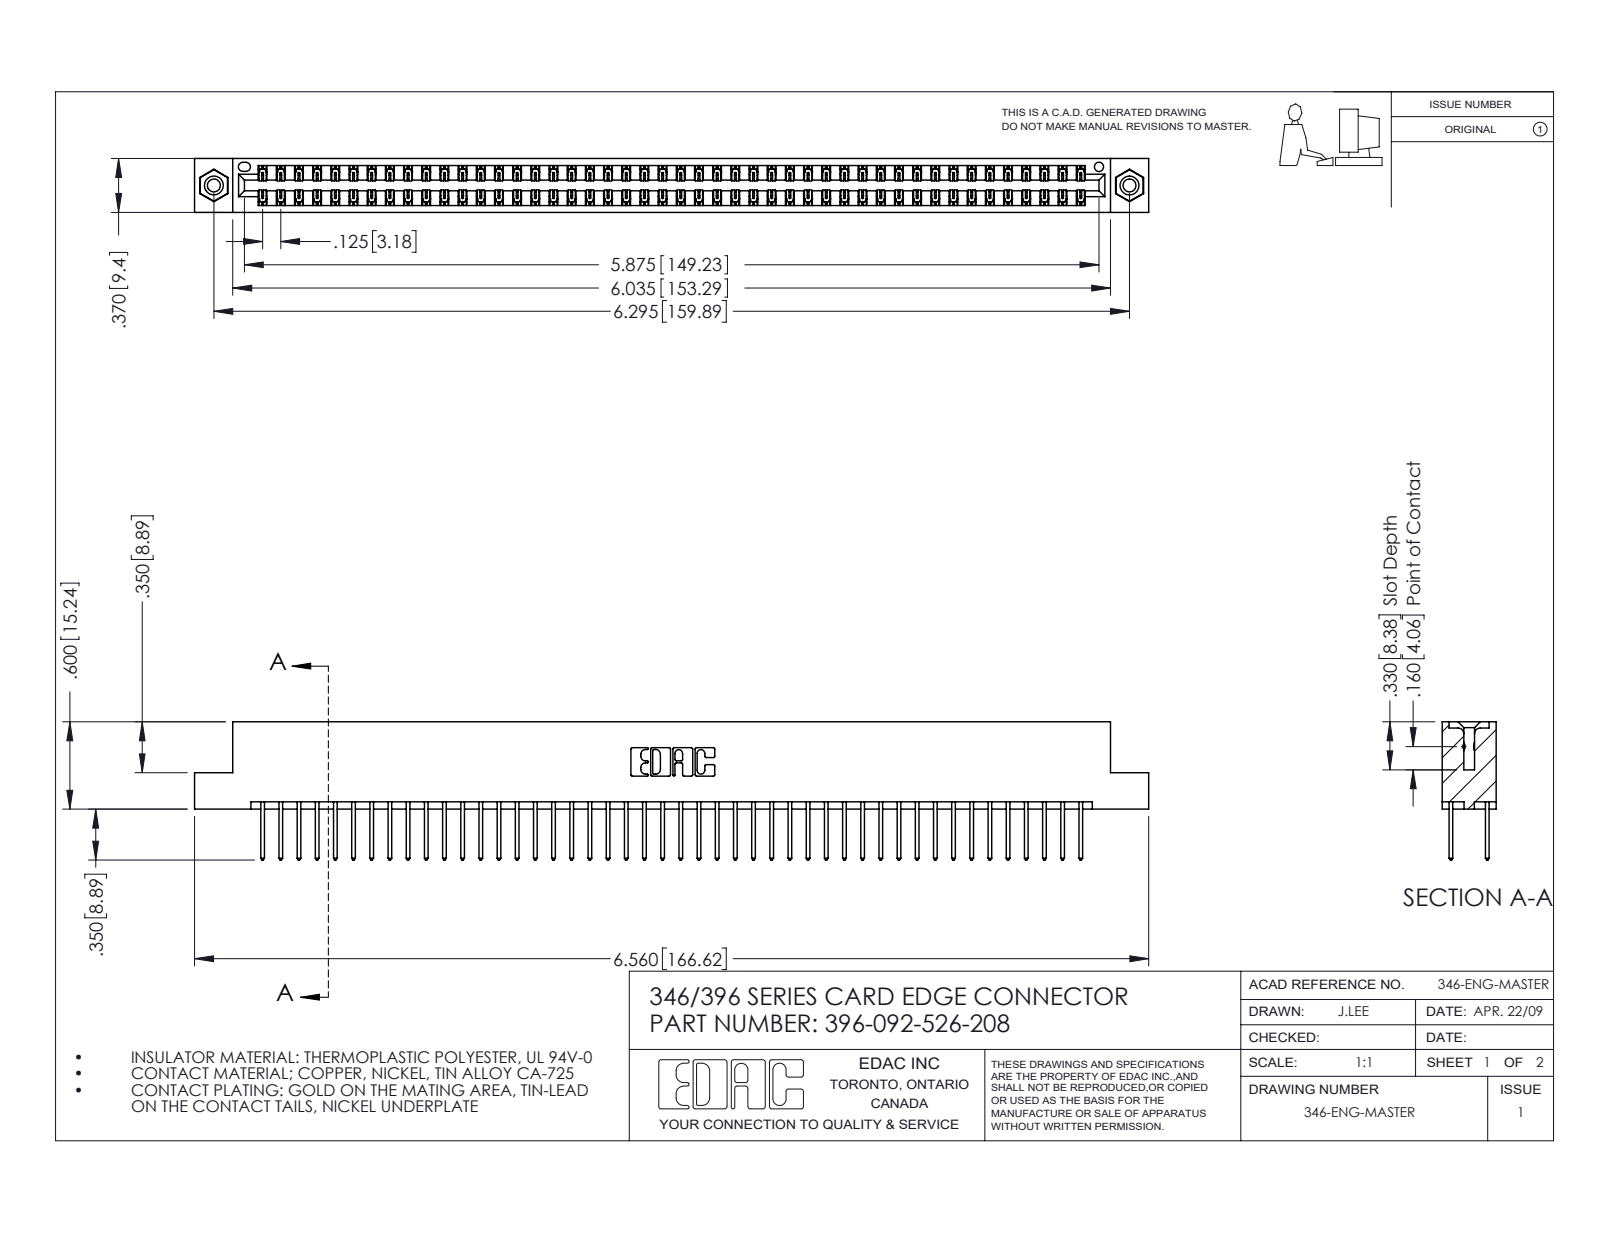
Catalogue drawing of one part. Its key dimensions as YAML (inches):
part_name: "346 Part_Flush Mounting Lugs - 0.156 Dia-TI; 345-292-001_345-293-126; 345-250-001_345-250-003-102; 396-092-526-208"
step_written_by: "SolidWorks 2016 (CONFIG_CONTROL_DESIGN)"
units: inches
bodies: {solids: 95, faces: 4966, planar: 3328, cylindrical: 1622, other: 16}
overall_size: [6.56, 0.95, 0.37]
volume: 1.002
surface_area: 36.17
round_holes:
  - {diameter: 0.089, count: 2}
  - {diameter: 0.125, count: 2}
  - {diameter: 0.156, count: 2}
  - {diameter: 0.064, count: 1}
round_bosses_or_shafts:
  - {diameter: 0.155, count: 2}
partial_cylinders:
  - {radius: 0.006, count: 138}
  - {radius: 0.01, count: 92}
  - {radius: 0.01, count: 22}
  - {radius: 0.007, count: 6}
  - {radius: 0.031, count: 6}
  - {radius: 0.026, count: 3}
  - {radius: 0.014, count: 2}
  - {radius: 0.022, count: 2}
face_to_face_distances: [0.048, 0.322, 0.25, 0.37, 0.072, 0.298, 0.025, 0.275, 0.148, 0.222]
hole_center_spacings: [0.246, 6.086, 6.295]
